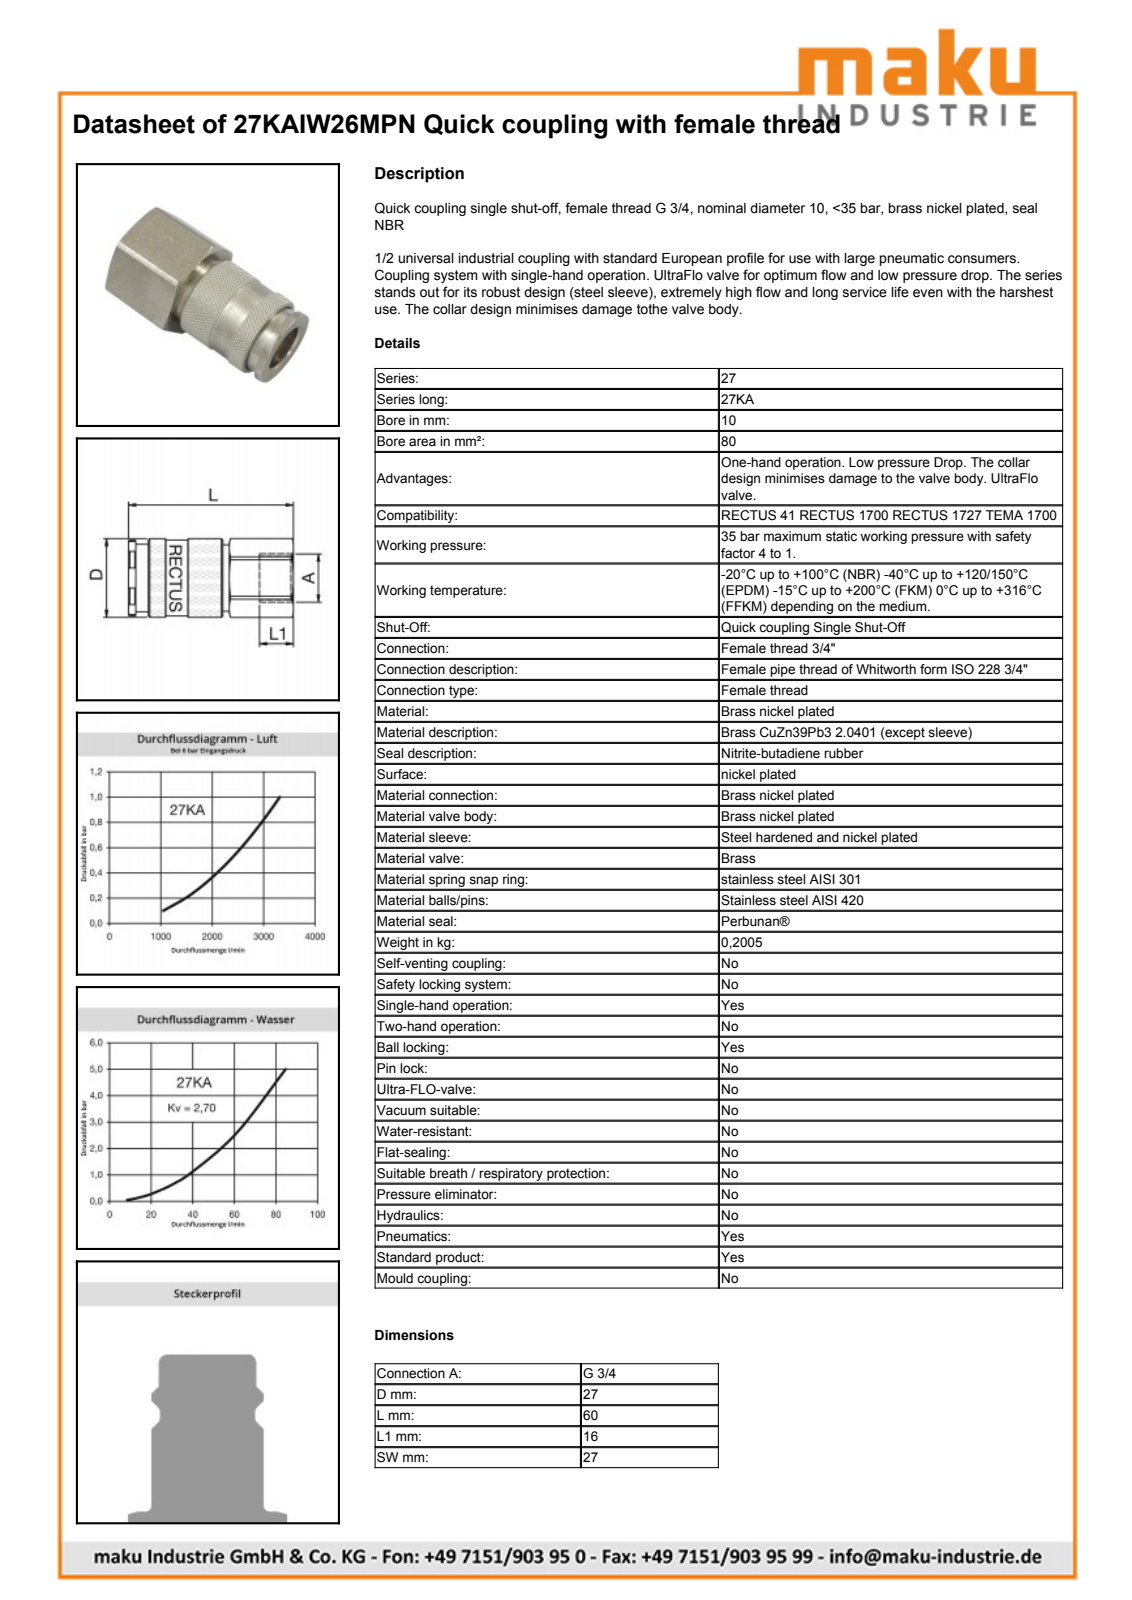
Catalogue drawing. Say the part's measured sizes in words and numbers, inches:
The part is named "D111282". Its 3-D file was written by "Autodesk Inventor 2013 (AUTOMOTIVE_DESIGN)". It is 2 solids with 491 faces: 190 planar, 63 cylindrical and 238 other. Overall it measures 2.38 by 1.421 by 1.294 inches. Its volume is 1.954 cubic inches and its surface area 20.06 square inches. Round holes: 1 of diameter 0.799, 1 of diameter 0.825, 1 of diameter 0.919, 1 of diameter 0.927, 1 of diameter 0.95. Round bosses or shafts: 1 of diameter 1.069, 1 of diameter 1.024, 1 of diameter 0.909, 1 of diameter 0.896, 1 of diameter 0.789. Partial cylindrical surfaces (rounded edges, fillets, slot ends): 1 of radius 0.508, 1 of radius 0.711. The main face-to-face distances are 1.26, 1.261, 1.358, 1.75, 0.392, 0.63, 2.38, 1.022, 1.75, 0.392.
